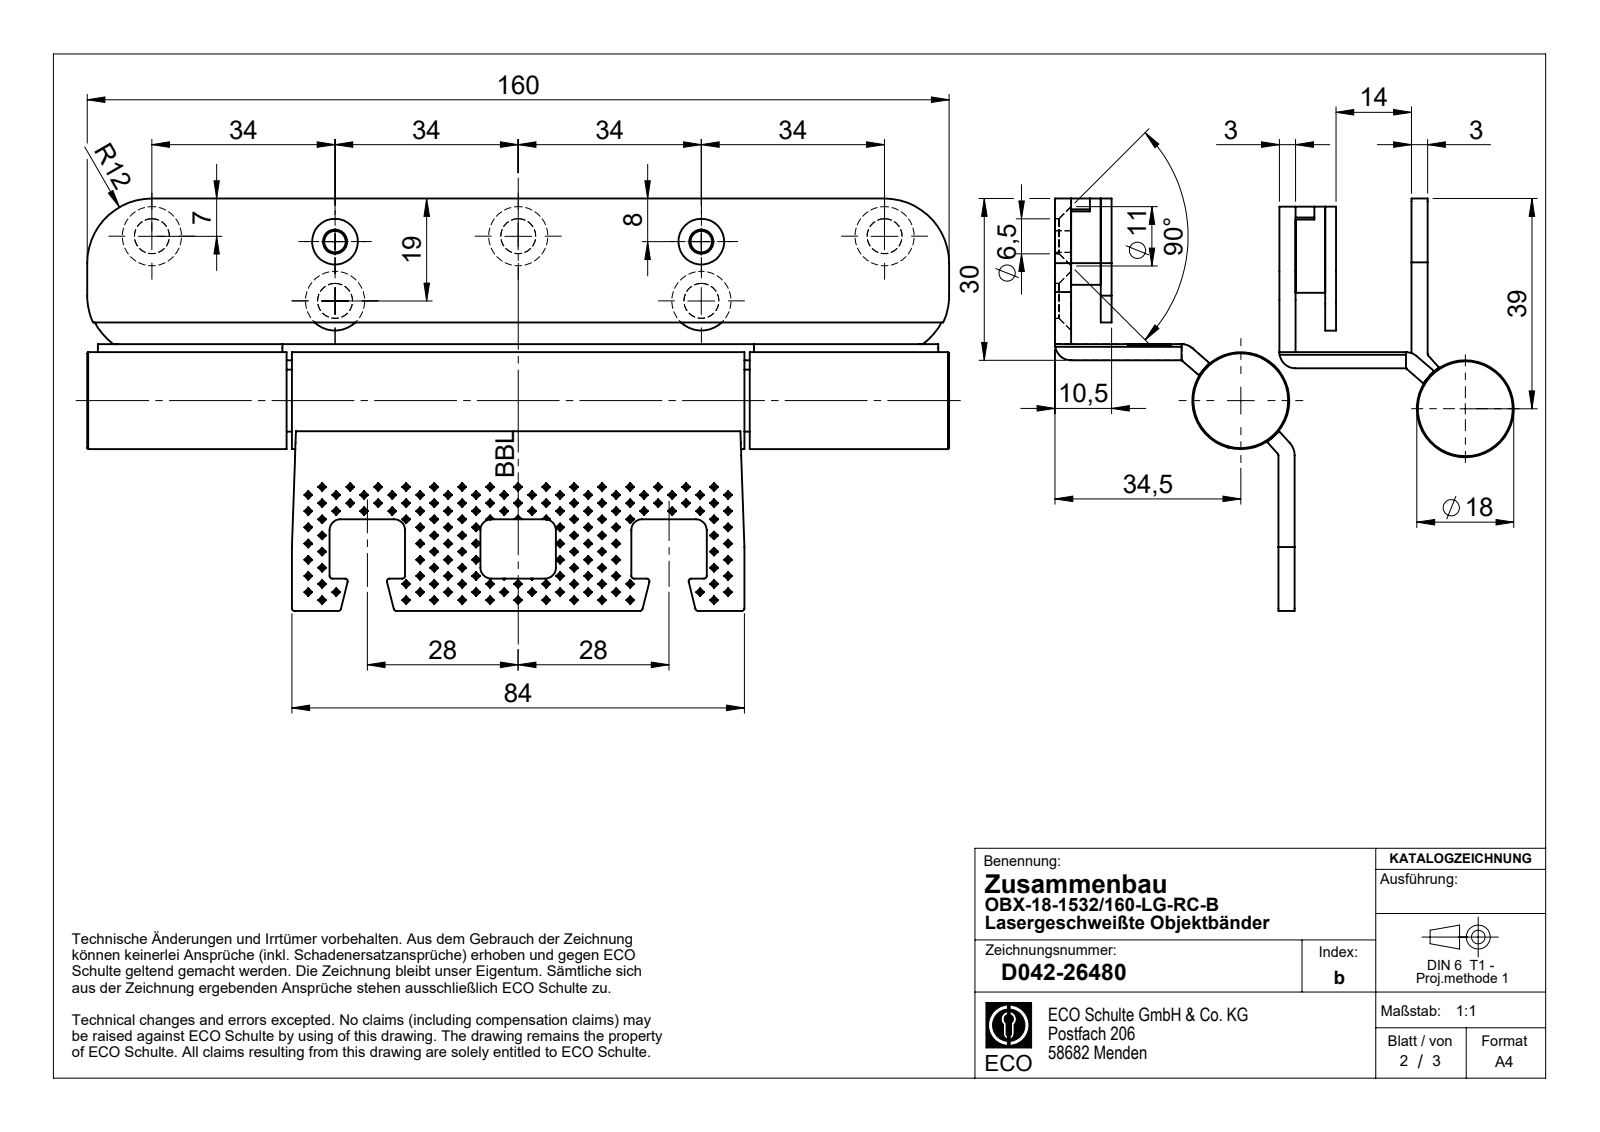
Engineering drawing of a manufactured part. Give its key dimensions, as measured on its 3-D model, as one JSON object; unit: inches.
{"part_name": "D043-19098; B01572; OBX-18-1532-160-LG-RC-B_D042-26480; D043-25252 (+6 more)", "step_written_by": "SolidWorks 2020 (CONFIG_CONTROL_DESIGN)", "units": "inches", "bodies": {"solids": 13, "faces": 1864, "planar": 1590, "cylindrical": 173, "other": 101}, "overall_size": [6.299, 1.89, 1.713], "volume_in3": 5.094, "surface_area_in2": 86.51, "round_holes": [[0.256, 5], [0.079, 2], [0.157, 2], [0.197, 2], [0.02, 1], [0.177, 1], [0.311, 1]], "round_bosses_or_shafts": [[0.276, 2], [0.709, 1], [0.472, 1], [0.465, 1], [0.453, 1], [0.303, 1], [0.157, 1], [0.065, 1]], "partial_cylinders_radius": [[0.02, 15], [0.079, 8], [0.01, 6], [0.472, 6], [0.138, 5], [0.098, 4], [0.027, 2], [0.083, 2]], "face_to_face_distances": [0.118, 0.079, 0.217, 0.335, 0.295, 0.965, 0.413, 0.551, 0.63, 0.157], "hole_center_spacings": [1.339, 1.42, 2.677, 0.433, 2.712, 4.016, 4.043, 0.077]}
